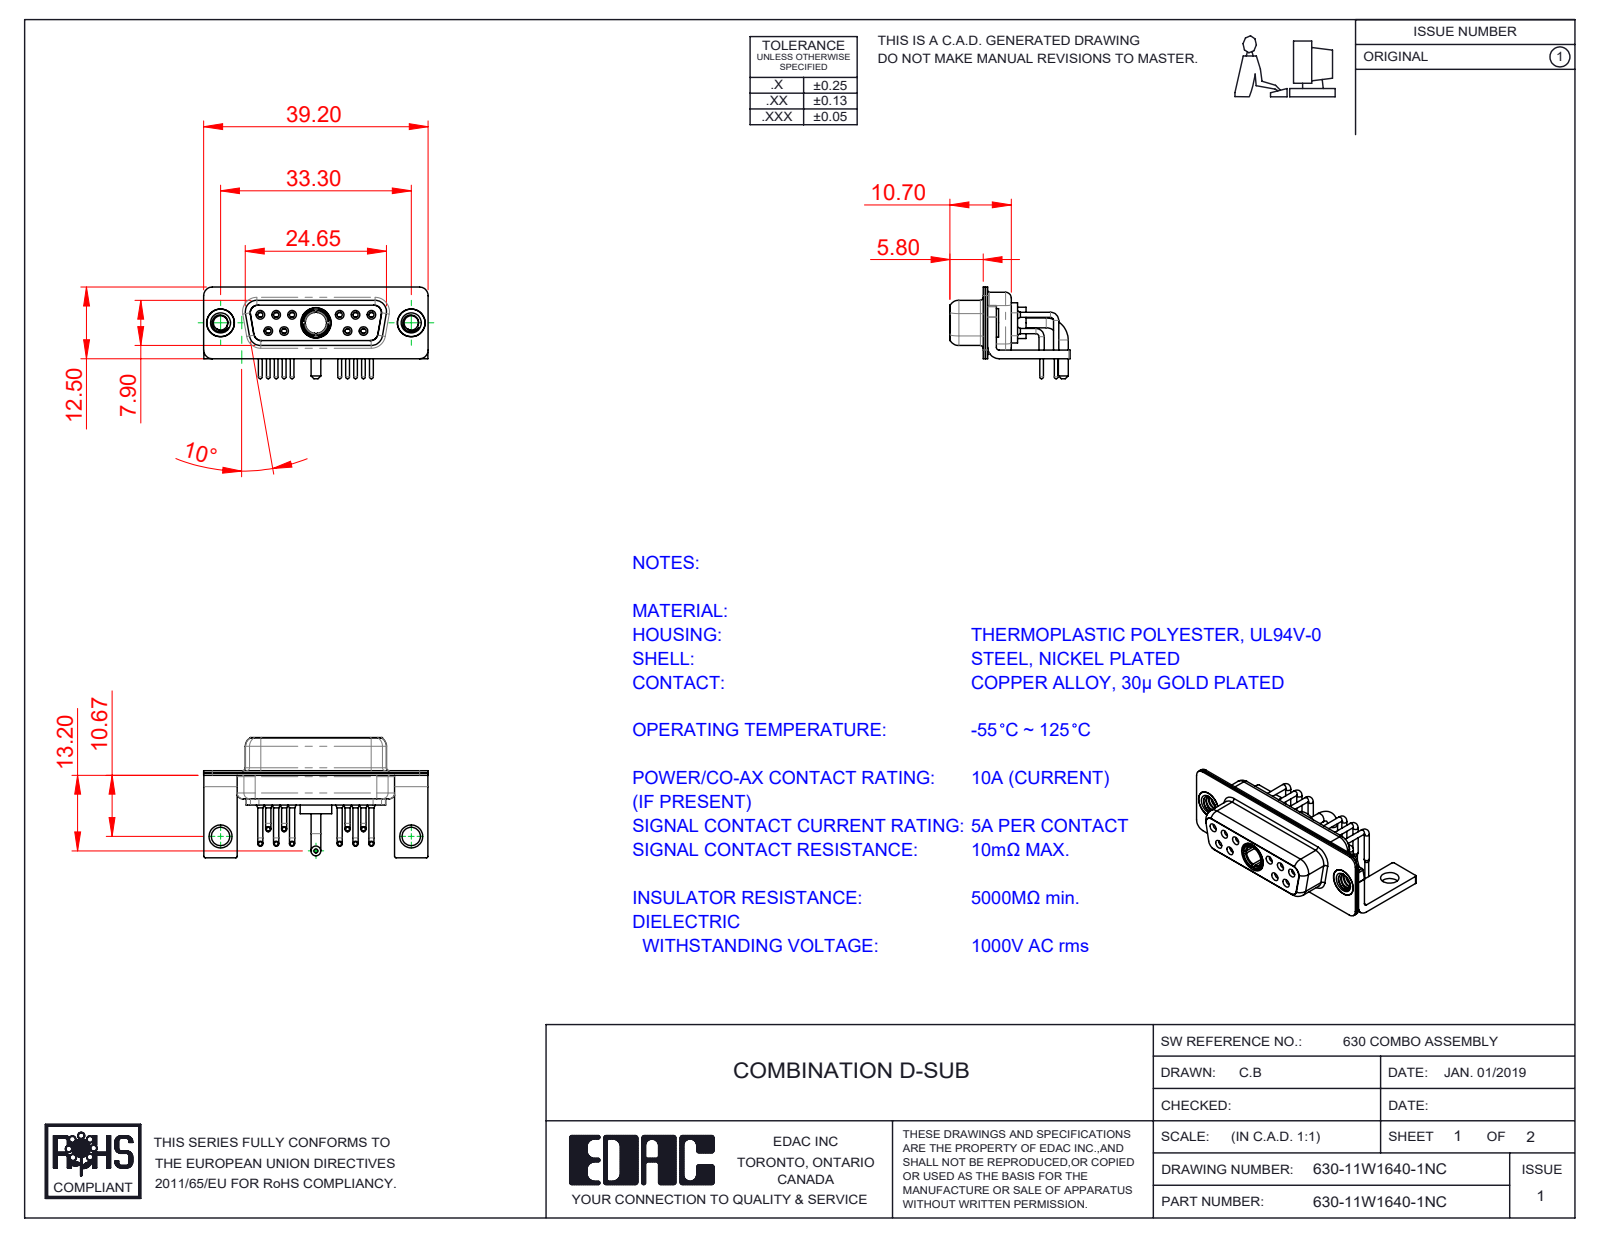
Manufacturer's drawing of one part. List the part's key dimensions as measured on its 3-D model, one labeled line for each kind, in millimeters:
Part name (STEP PRODUCT): 630Combo Contact Row 2; 630Combo Contact Row 1; 630Combo Shell Front_15 Contacts; 630-11W1640-1NC (+5 more)
STEP written by: SolidWorks 2020 (CONFIG_CONTROL_DESIGN)
Units: millimetres
Bodies: 19 solids, 925 faces (266 planar, 410 cylindrical, 249 other)
Overall size (bounding box): 39.2 × 21 × 16
Volume: 2 850 mm³ · Surface area: 6 809 mm²
Round holes (diameter × count): ⌀0.9 ×10, ⌀1.1 ×10, ⌀1.5 ×10, ⌀2 ×10, ⌀1.7 ×6, ⌀1.6 ×4, ⌀4.85 ×3, ⌀2.5 ×2, ⌀3.2 ×2, ⌀4 ×2, ⌀4.05 ×2, ⌀3.7 ×1
Round bosses / shafts (diameter × count): ⌀0.9 ×10, ⌀0.65 ×10, ⌀1.6 ×6, ⌀5 ×2, ⌀4.95 ×2, ⌀4.8 ×2, ⌀1.7 ×2, ⌀5.5 ×1
Partial cylindrical surfaces — rounded edges, fillets, slot ends (radius × count): R0.25 ×16, R1.5 ×16, R2 ×13, R1.35 ×12, R1.6 ×8, R0.5 ×5, R0.6 ×4, R0.65 ×4
Main face-to-face distances: 0.4, 0.8, 1.4, 0.45, 8.45, 1.5, 1.8, 8.9, 6.2, 2.3
Hole centre spacings: 3.16, 2.77, 13.85, 11.08, 16.62, 5.03, 5.04, 5.54
